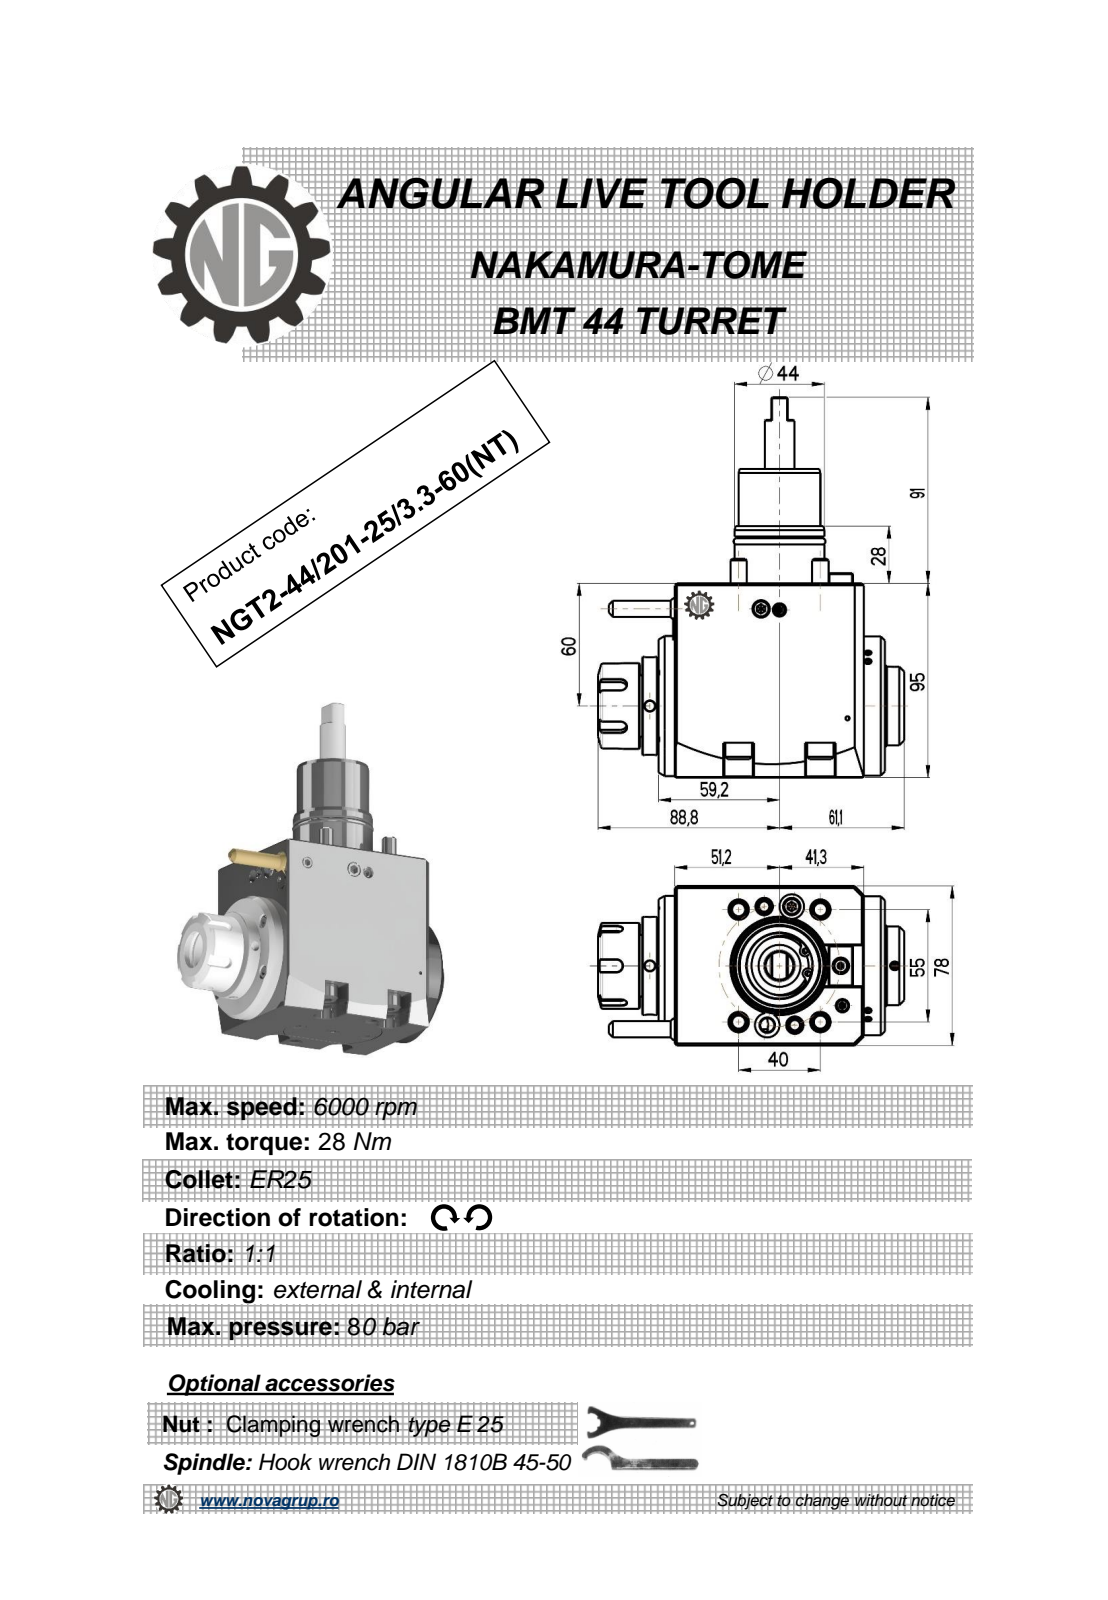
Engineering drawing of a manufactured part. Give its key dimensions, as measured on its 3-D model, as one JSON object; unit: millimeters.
{"part_name": "NGT2_44_201_25_3_3_60_NT", "step_written_by": "PRO/ENGINEER BY PARAMETRIC TECHNOLOGY CORPORATION, 2010280 (CONFIG_CONTROL_DESIGN)", "units": "millimeters", "bodies": {"solids": 2, "faces": 399, "planar": 167, "cylindrical": 109, "other": 123}, "overall_size": [186, 149.9, 78], "volume_mm3": 871465, "surface_area_mm2": 74852, "round_holes": [[5, 3], [6.8, 2], [3, 1], [20.3, 1]], "round_bosses_or_shafts": [[8, 5], [13, 4], [68.5, 1], [68, 1], [48, 1], [44, 1], [42, 1], [40, 1]], "partial_cylinders_radius": [[0.26, 20], [0.22, 6], [3, 5], [7, 4], [0.8, 2], [390, 2]], "face_to_face_distances": [78, 95, 8, 92.5, 100.5, 110.8, 102.8, 10.3, 16, 56], "hole_center_spacings": [56.72, 59.23, 64.35, 75.26]}
